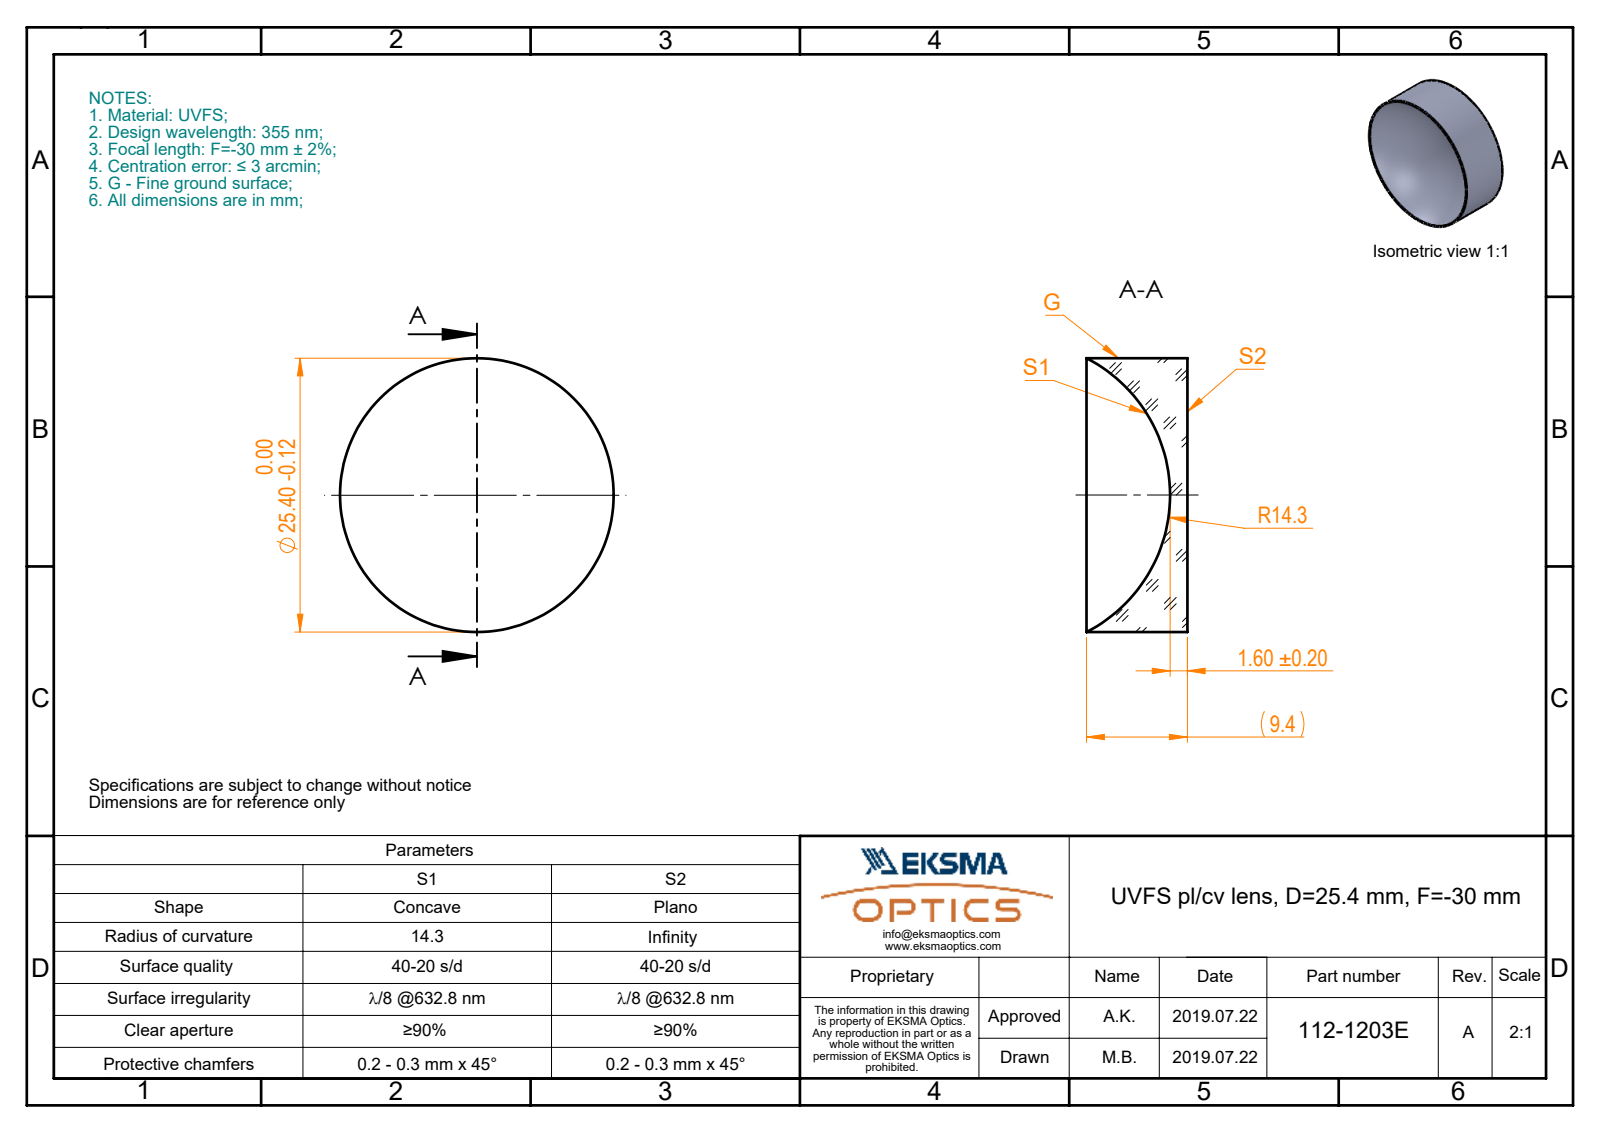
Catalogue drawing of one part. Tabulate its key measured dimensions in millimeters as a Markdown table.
| quantity | value |
| --- | --- |
| part name | 112-1203E UVFS pl-cv 12.7 F-30 |
| STEP written by | SolidWorks 2017 (CONFIG_CONTROL_DESIGN) |
| units | millimeters |
| bodies | 1 solid, 5 faces (1 planar, 2 cylindrical, 2 other) |
| overall size | 25.4 × 25.4 × 9.35 |
| volume | 2 531 mm³ |
| surface area | 1 948 mm² |
| round bosses / shafts (diameter × count) | 25.4 × 1 |
